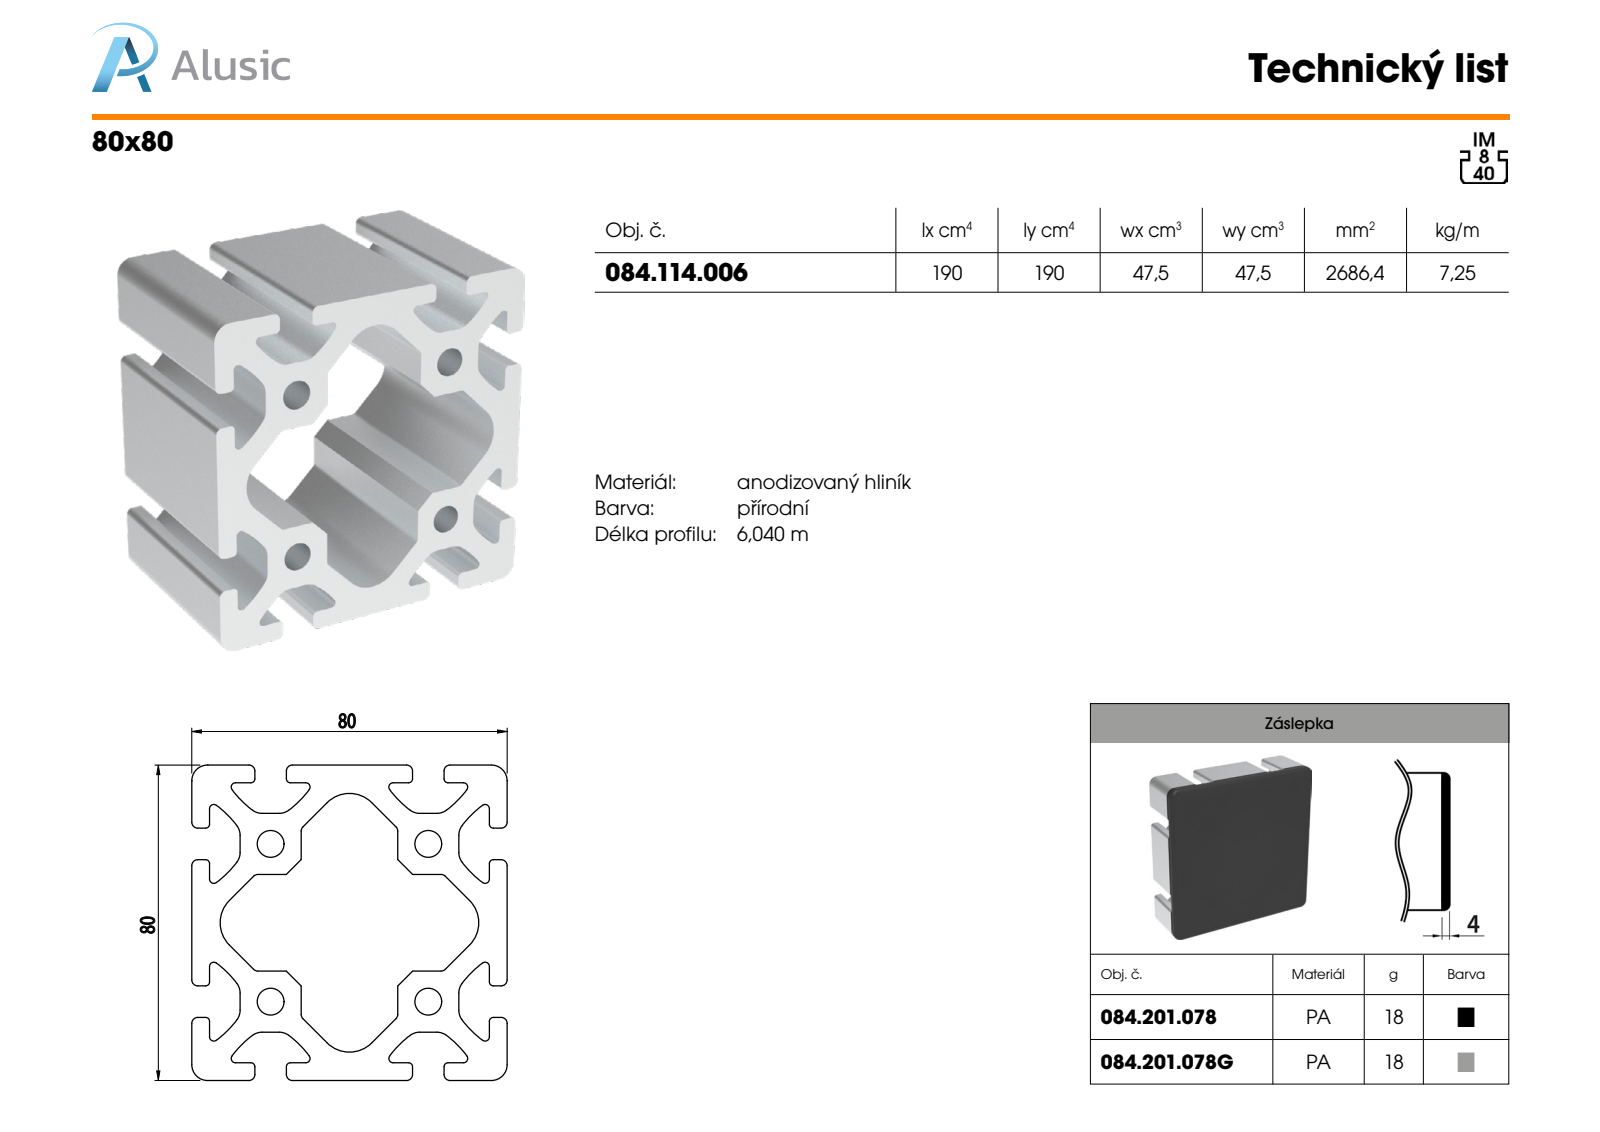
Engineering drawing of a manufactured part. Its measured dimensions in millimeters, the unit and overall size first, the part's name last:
Units: millimetres
Overall size (bounding box): 100 × 80 × 80
Round holes (diameter × count): ⌀6.8 ×4
Partial cylindrical surfaces — rounded edges, fillets, slot ends (radius × count): R1.5 ×24, R4 ×20, R1 ×16, R1.08 ×16, R25 ×16, R8 ×4
Main face-to-face distances: 80, 4.5, 75.5, 27.75, 52.25, 23.25, 47.75, 40, 12.25, 67.75
Hole centre spacings: 40, 56.57
Volume: 268 280 mm³ · Surface area: 96 149 mm²
Bodies: 1 solid, 183 faces (74 planar, 109 cylindrical, 0 other)
Part name (STEP PRODUCT): 084.114.006
STEP written by: SolidWorks 2018 (AUTOMOTIVE_DESIGN)
